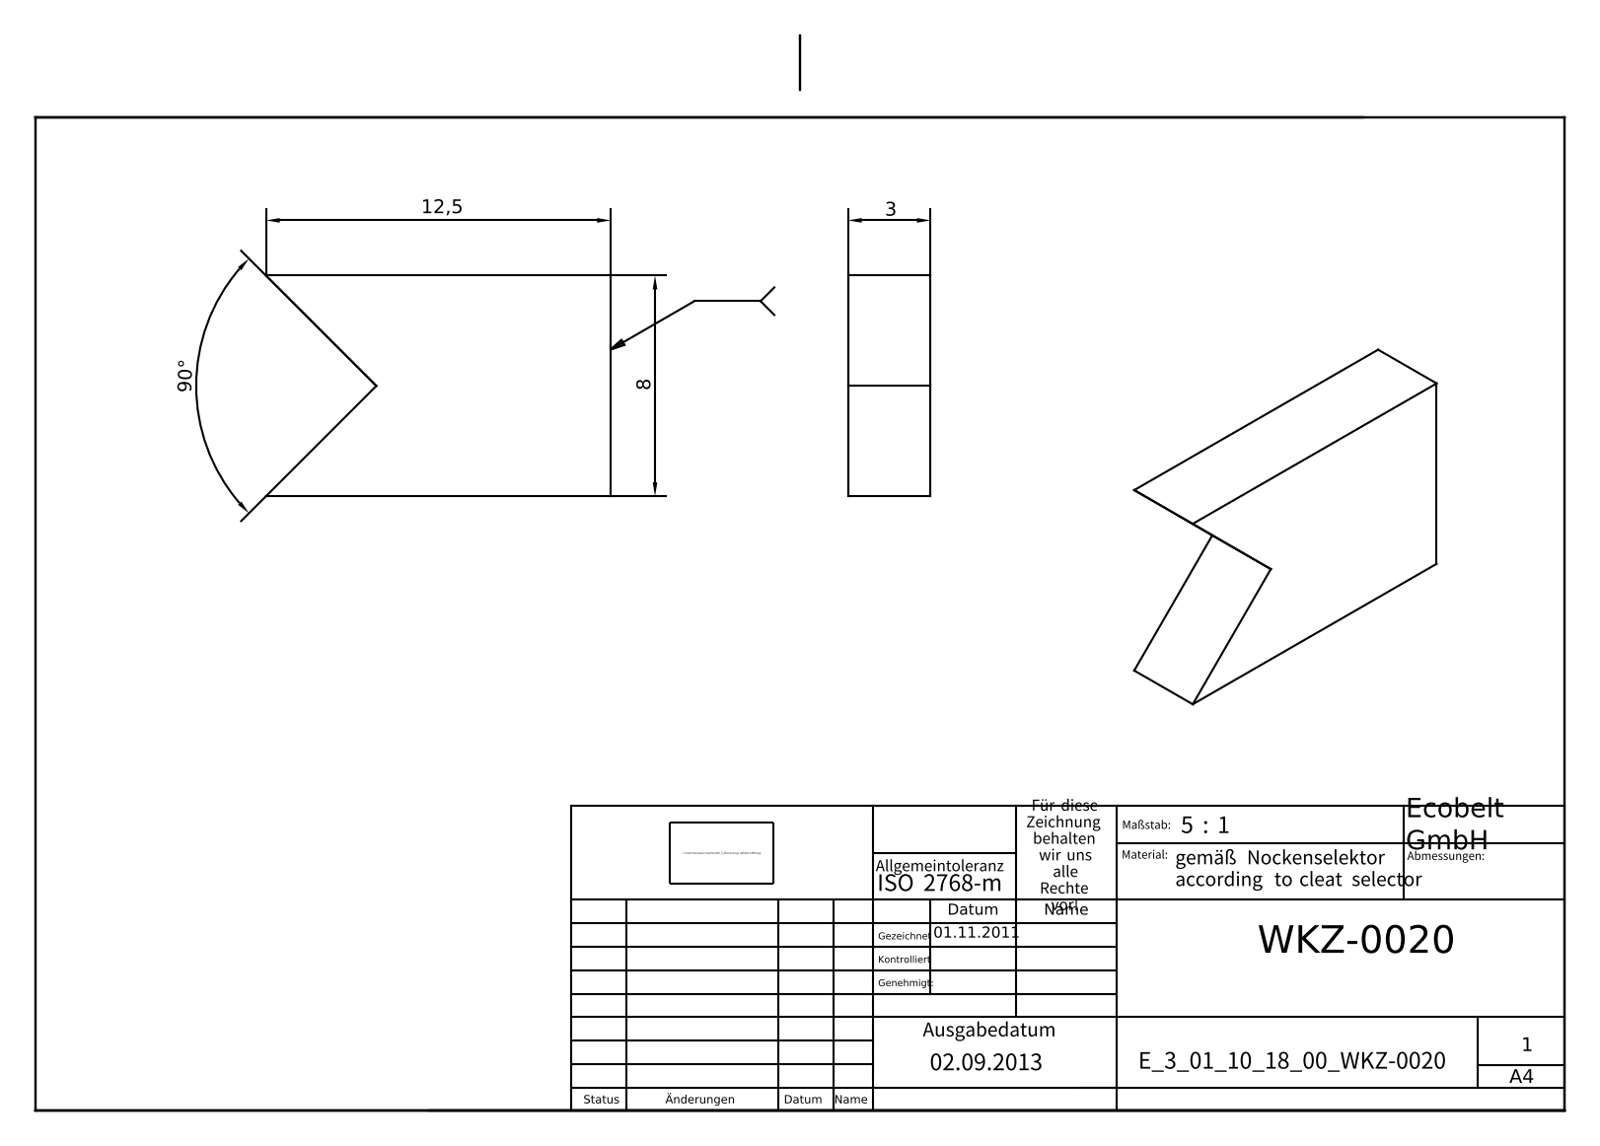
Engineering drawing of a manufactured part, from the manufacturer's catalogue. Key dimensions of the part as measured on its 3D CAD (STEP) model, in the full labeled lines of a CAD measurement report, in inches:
Part name (STEP PRODUCT): E_3_01_10_18_00_WKZ-0020
STEP written by: Autodesk Inventor 2021 (AUTOMOTIVE_DESIGN)
Units: inches
Bodies: 1 solid, 7 faces (7 planar, 0 cylindrical, 0 other)
Overall size (bounding box): 0.492 × 0.315 × 0.118
Volume: 0.015 in³ · Surface area: 0.467 in²
Main face-to-face distances: 0.118, 0.315
